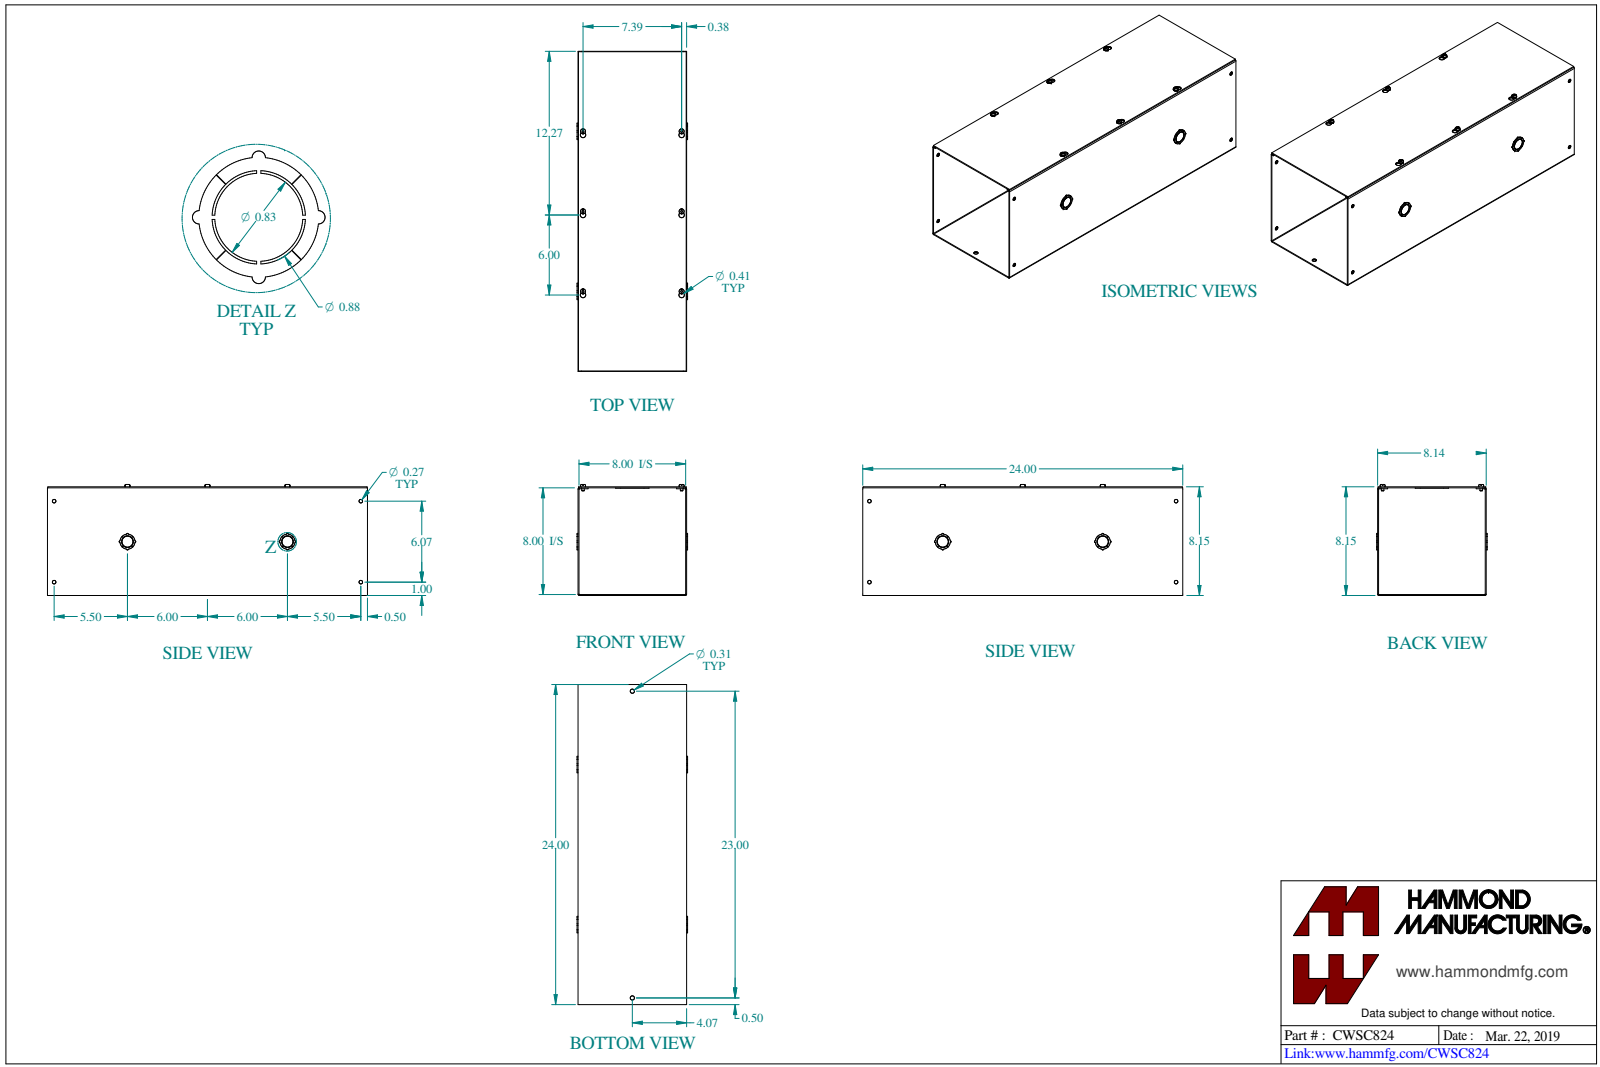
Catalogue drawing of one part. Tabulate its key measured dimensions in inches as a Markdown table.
| quantity | value |
| --- | --- |
| part name | CWSC824 |
| STEP written by | SolidWorks 2023 (CONFIG_CONTROL_DESIGN) |
| units | inches |
| bodies | 8 solids, 410 faces (186 planar, 188 cylindrical, 36 other) |
| overall size | 24 × 8.325 × 8.288 |
| volume | 59.07 in³ |
| surface area | 1 617 in² |
| round holes (diameter × count) | 0.177 × 6, 0.266 × 4, 0.313 × 2, 0.875 × 2 |
| round bosses / shafts (diameter × count) | 0.375 × 6, 0.19 × 6, 1.125 × 2, 0.825 × 2 |
| partial cylindrical surfaces (radius × count) | 0.063 × 8, 0.125 × 6, 0.203 × 6, 0.036 × 4, 0.108 × 4 |
| main face-to-face distances | 0.072, 8.072, 8, 0.078, 8.144, 8.15, 8.078, 7.928, 0.15, 0.031 |
| hole center spacings | 6, 6.282, 6.627, 9.522, 12.08, 17.761, 17.886, 7.394 |
